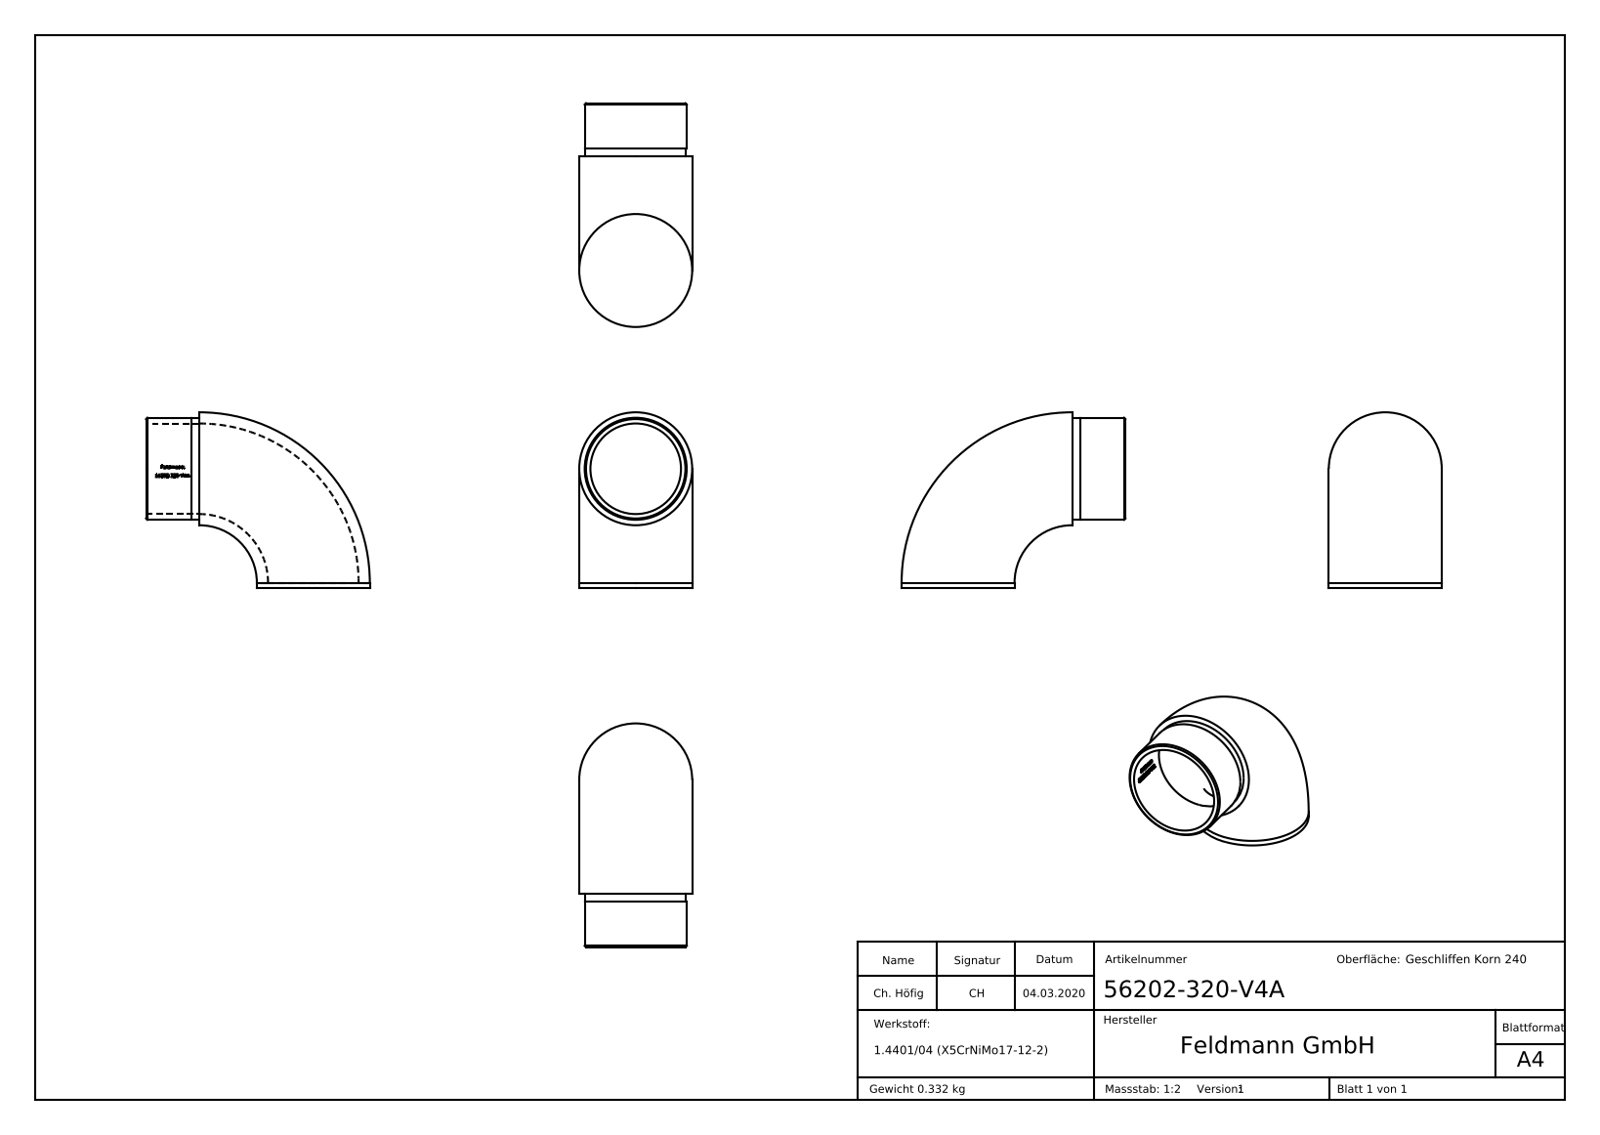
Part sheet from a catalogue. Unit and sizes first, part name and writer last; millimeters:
Units: millimetres
Overall size (bounding box): 84 × 66 × 42.4
Round holes (diameter × count): ⌀34 ×1
Round bosses / shafts (diameter × count): ⌀42.4 ×1, ⌀38.3 ×1, ⌀37.9 ×1
Partial cylindrical surfaces — rounded edges, fillets, slot ends (radius × count): R17.1 ×1
Main face-to-face distances: 2, 20, 3, 17, 1.32, 41.6, 39.6, 4.09, 2.97, 3.36
Volume: 41 506 mm³ · Surface area: 23 790 mm²
Bodies: 1 solid, 279 faces (128 planar, 33 cylindrical, 118 other)
Part name (STEP PRODUCT): 56202-320-V4A
STEP written by: SolidWorks 2015 (CONFIG_CONTROL_DESIGN)
